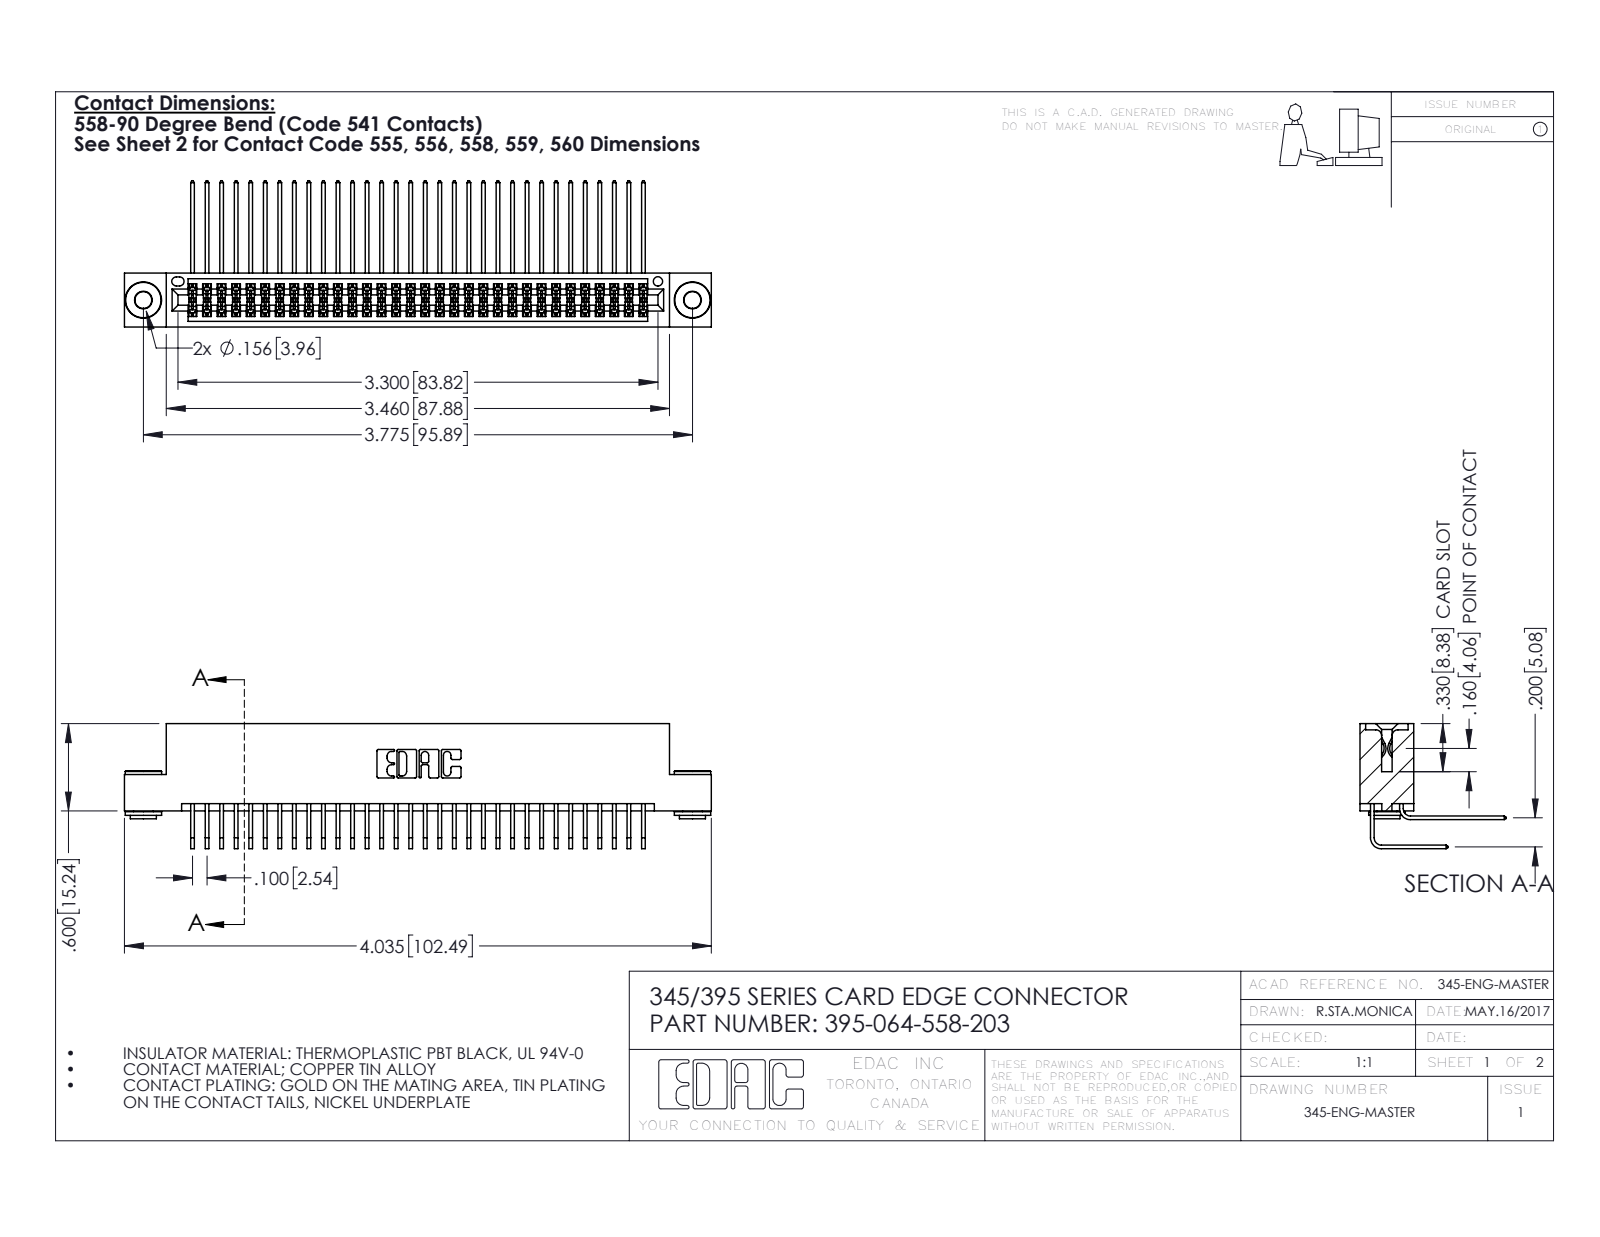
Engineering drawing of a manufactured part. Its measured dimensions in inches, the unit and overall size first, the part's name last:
Units: inches
Overall size (bounding box): 4.035 × 1.005 × 0.859
Round holes (diameter × count): ⌀0.116 ×2, ⌀0.156 ×2, ⌀0.064 ×1
Round bosses / shafts (diameter × count): ⌀0.25 ×2, ⌀0.18 ×2, ⌀0.136 ×2
Partial cylindrical surfaces — rounded edges, fillets, slot ends (radius × count): R0.006 ×97, R0.01 ×22, R0.007 ×6, R0.031 ×6, R0.026 ×3, R0.014 ×2, R0.019 ×2, R0.022 ×2
Main face-to-face distances: 0.2, 0.072, 0.298, 0.37, 0.025, 0.098, 0.272, 0.225, 0.025, 0.285
Hole centre spacings: 0.27, 3.54, 3.775
Volume: 0.626 in³ · Surface area: 26.2 in²
Bodies: 67 solids, 3492 faces (2330 planar, 1154 cylindrical, 8 other)
Part name (STEP PRODUCT): 345-250-002_345-250-002-102; 395-064-558-203; 345-292-001_558 Tail - 2; 345 Part_Flush Mounting Lugs - 0.156 Dia-TH (+1 more)
STEP written by: SolidWorks 2016 (CONFIG_CONTROL_DESIGN)
